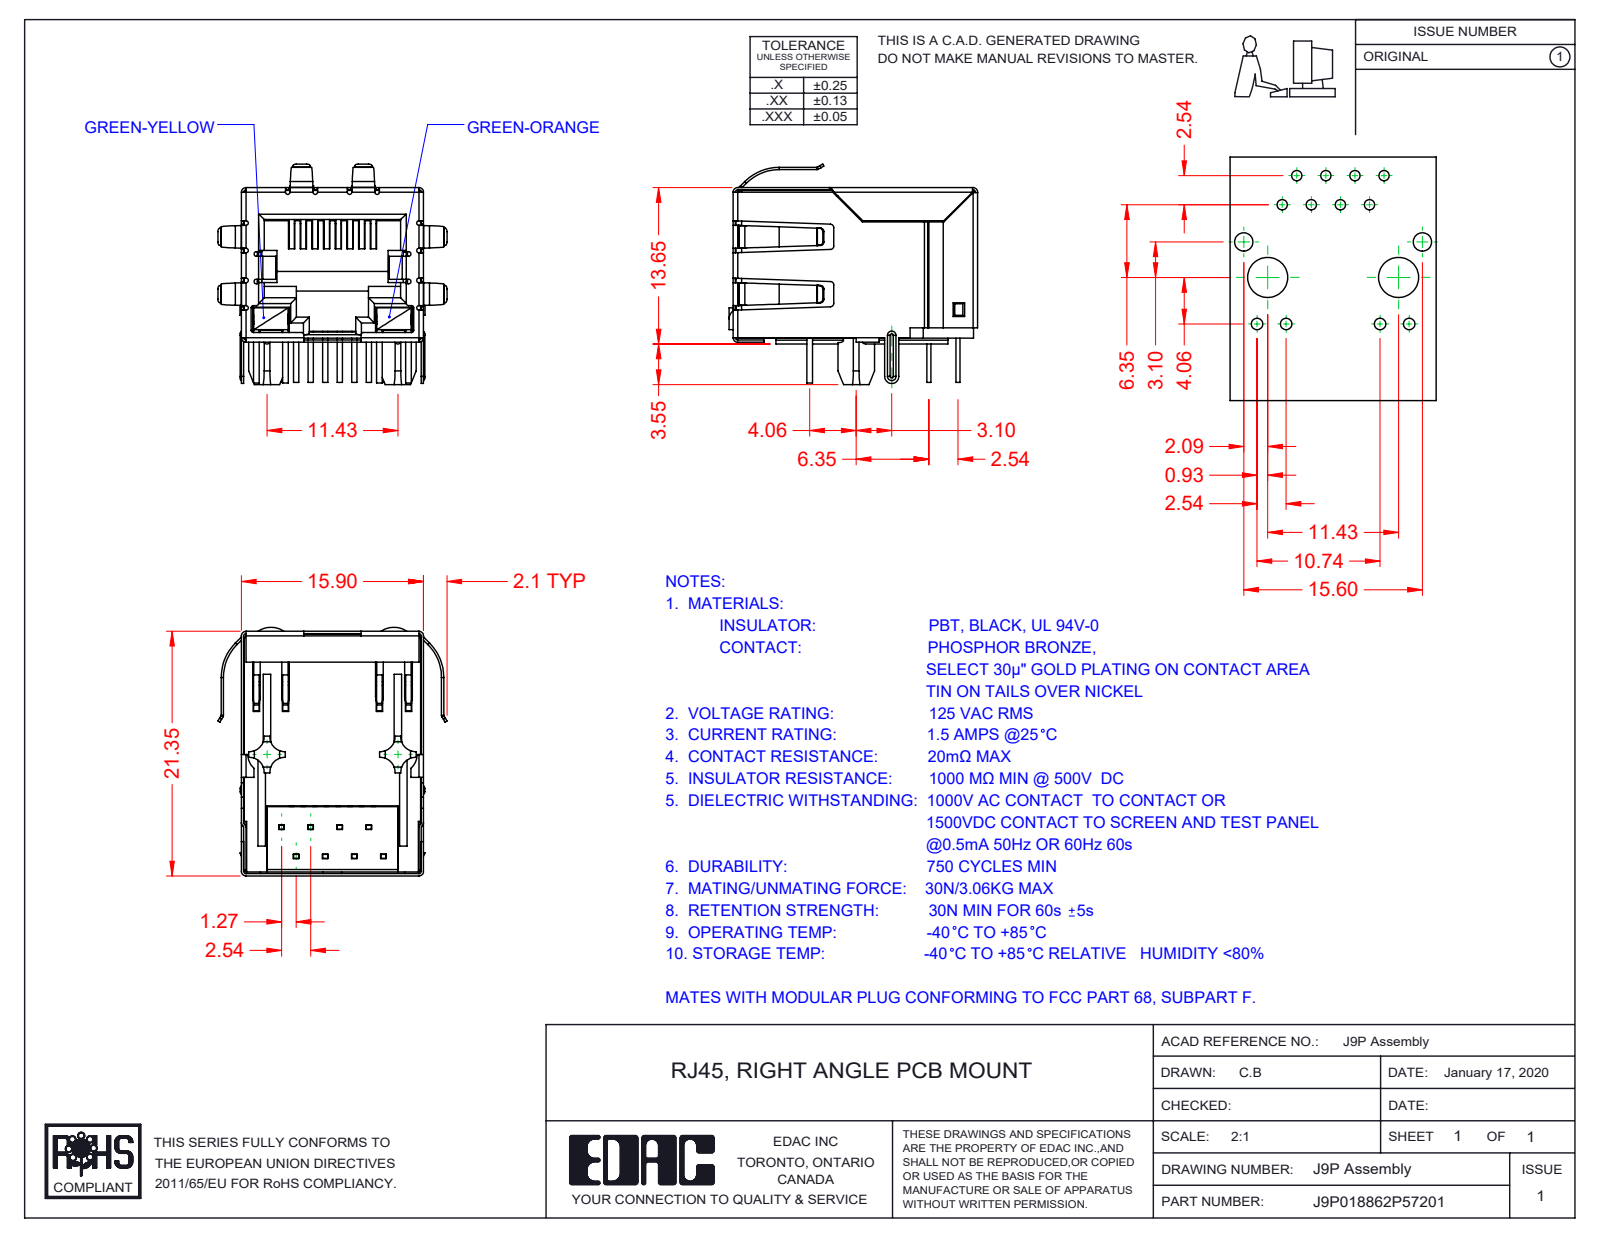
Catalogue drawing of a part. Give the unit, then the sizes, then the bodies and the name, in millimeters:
Units: millimetres
Overall size (bounding box): 21.7 × 20 × 19.25
Partial cylindrical surfaces — rounded edges, fillets, slot ends (radius × count): R0.2 ×39, R0.5 ×22, R0.3 ×20, R0.4 ×16, R1.3 ×8, R0.23 ×5, R0.11 ×4, R0.31 ×4
Main face-to-face distances: 15.45, 15.7, 15.65, 0.35, 0.54, 15.5, 12.36, 0.6, 1.4, 0.59
Volume: 2 687 mm³ · Surface area: 7 515 mm²
Bodies: 13 solids, 1476 faces (1042 planar, 340 cylindrical, 94 other)
Part name (STEP PRODUCT): 9P-LED LED RH_7-Green-Orange; 9P-LED Shield; J9P018862P57202; 9P-LED LED LH_5-Green-Yellow (+4 more)
STEP written by: SolidWorks 2016 (CONFIG_CONTROL_DESIGN)
